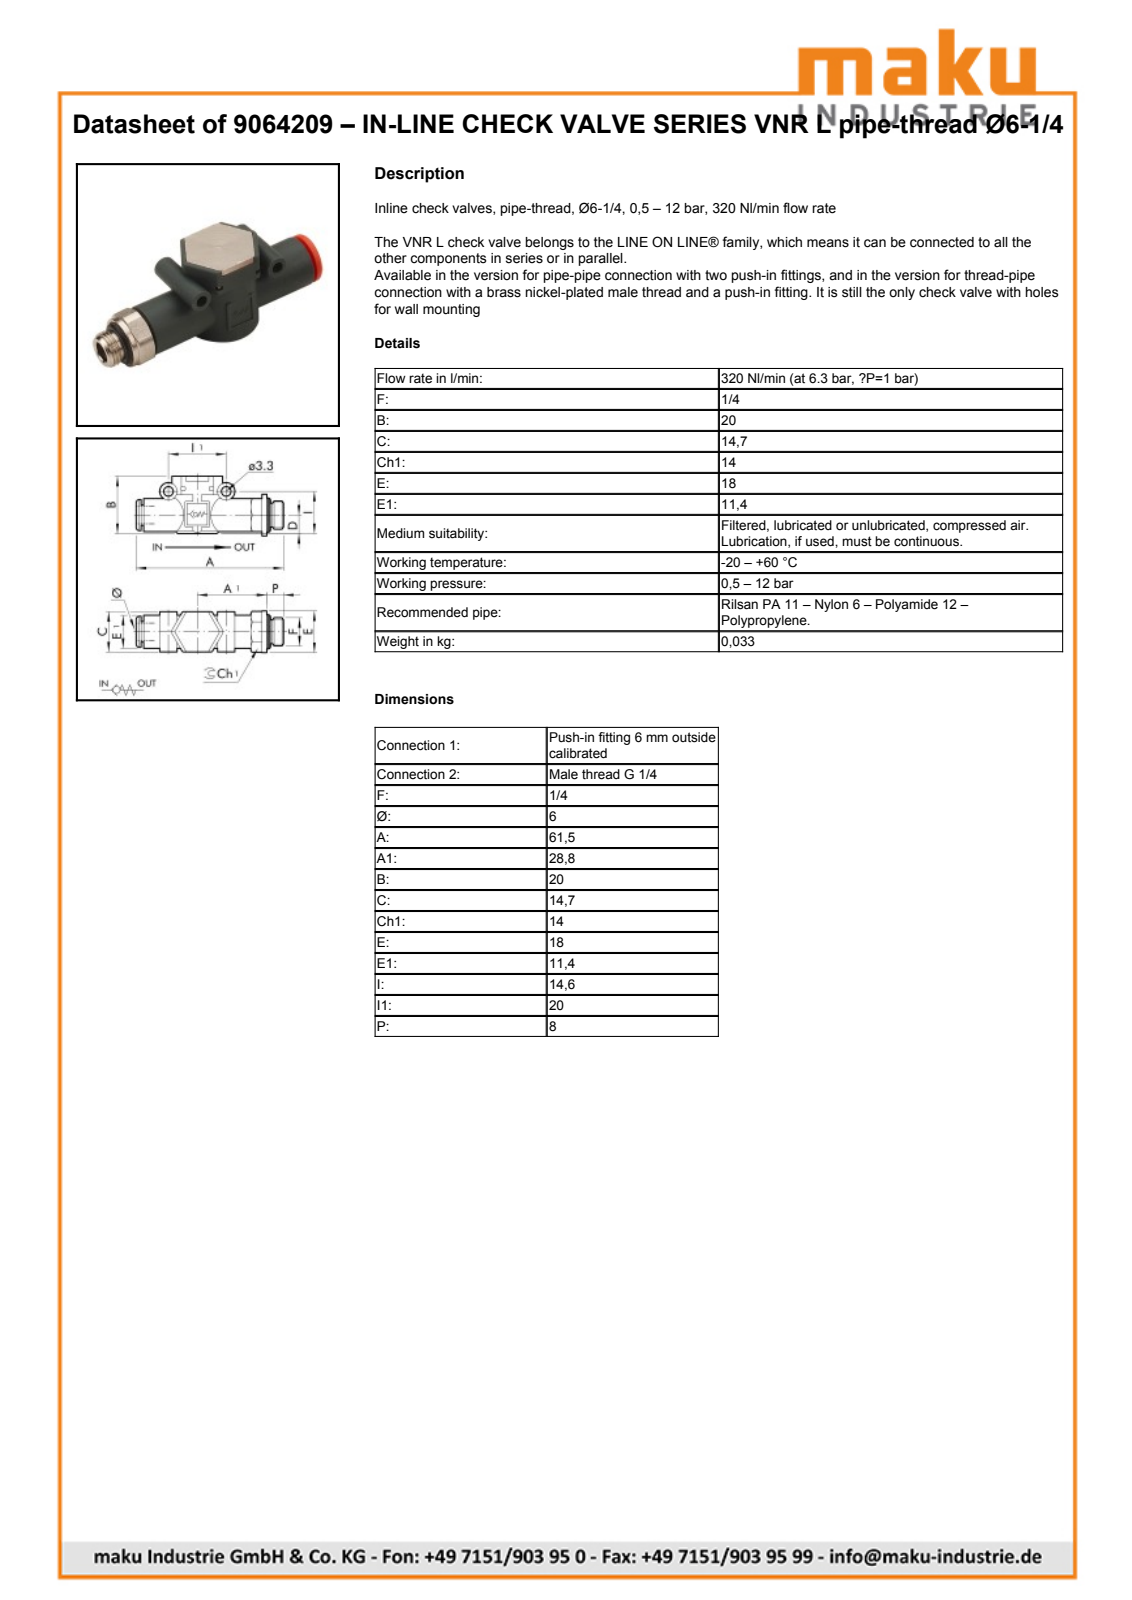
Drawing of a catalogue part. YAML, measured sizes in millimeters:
part_name: "9064209; LINE-ON-LINE D6 VSR-L body; LINE-ON-LINE D6-1/4 thread port; LINE-ON-LINE D6 VNR-L bushing (+1 more)"
step_written_by: "PARTsolutions (AUTOMOTIVE_DESIGN)"
units: millimeters
bodies: {solids: 4, faces: 146, planar: 84, cylindrical: 51, other: 11}
overall_size: [61.3, 22.6, 18]
volume: 6311
surface_area: 7330
round_holes:
  - {diameter: 3.3, count: 2}
  - {diameter: 3.5, count: 1}
  - {diameter: 4, count: 1}
  - {diameter: 6, count: 1}
  - {diameter: 6.2, count: 1}
  - {diameter: 7.4, count: 1}
  - {diameter: 8, count: 1}
  - {diameter: 9, count: 1}
  - {diameter: 9.6, count: 1}
  - {diameter: 10.3, count: 1}
  - {diameter: 11.6, count: 1}
round_bosses_or_shafts:
  - {diameter: 6, count: 2}
  - {diameter: 18, count: 1}
  - {diameter: 14.8, count: 1}
  - {diameter: 13.16, count: 1}
  - {diameter: 11.4, count: 1}
  - {diameter: 11.1, count: 1}
  - {diameter: 11, count: 1}
  - {diameter: 10, count: 1}
partial_cylinders:
  - {radius: 7.95, count: 2}
  - {radius: 3.75, count: 1}
  - {radius: 7.9, count: 1}
  - {radius: 9.15, count: 1}
face_to_face_distances: [1.6, 2, 14, 18.4, 20, 9.8, 1.04, 40.96, 1.4, 7.8]
hole_center_spacings: [12.74, 20]
